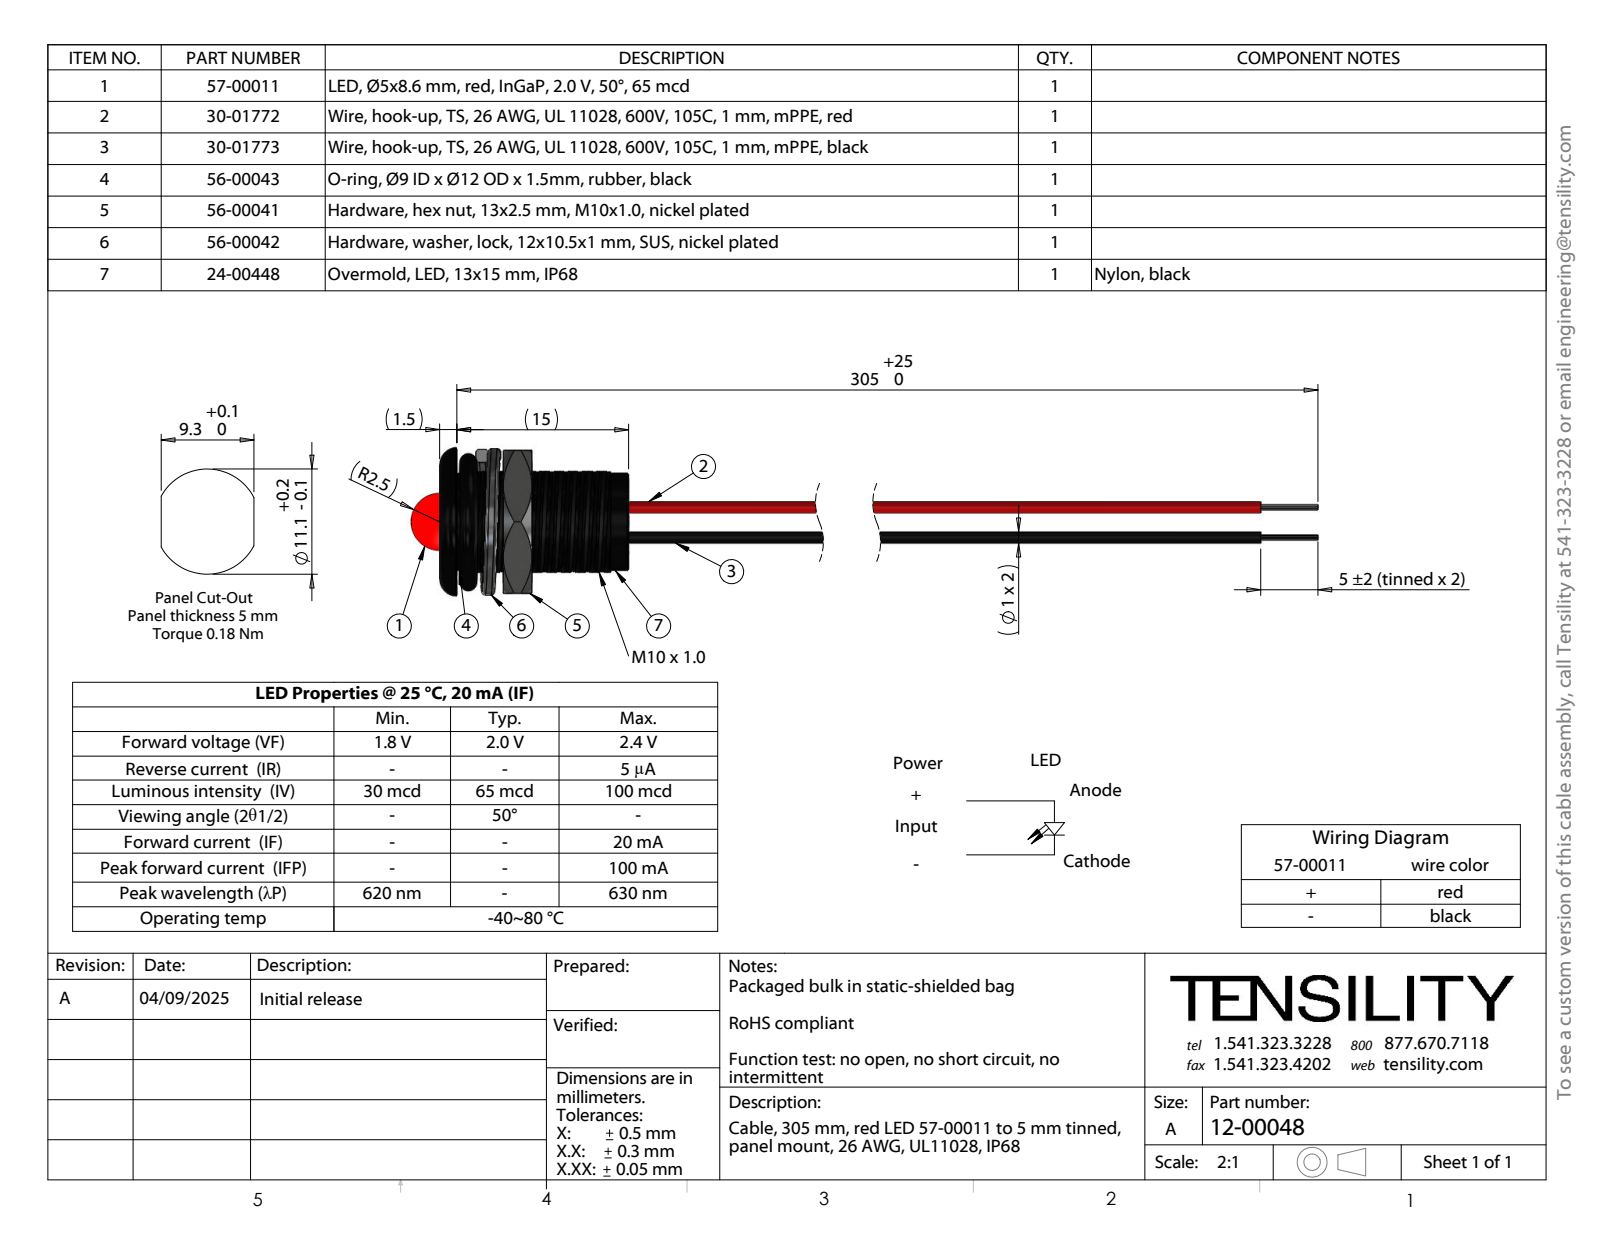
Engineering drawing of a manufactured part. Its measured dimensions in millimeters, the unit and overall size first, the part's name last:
Units: millimetres
Overall size (bounding box): 173.99 × 14.43 × 12.99
Round holes (diameter × count): ⌀1 ×2
Round bosses / shafts (diameter × count): ⌀1 ×2, ⌀0.83 ×2, ⌀8.5 ×1, ⌀5 ×1
Partial cylindrical surfaces — rounded edges, fillets, slot ends (radius × count): R4.33 ×1, R5 ×1
Main face-to-face distances: 1.5, 16.5, 15, 12.5, 8.06, 6.56, 8.44, 5.56, 4.06, 2.5
Hole centre spacings: 0.36, 0.38, 0.33, 2.43, 2.35, 2.48, 2.52, 2.56
Volume: 1 769 mm³ · Surface area: 6 568 mm²
Bodies: 57 solids, 514 faces (185 planar, 246 cylindrical, 83 other)
Part name (STEP PRODUCT): 24-00448; 30-01772_stripped and tinned; 57-00011_trimmed leads; 56-00041 (+4 more)
STEP written by: SolidWorks 2021 (CONFIG_CONTROL_DESIGN)
